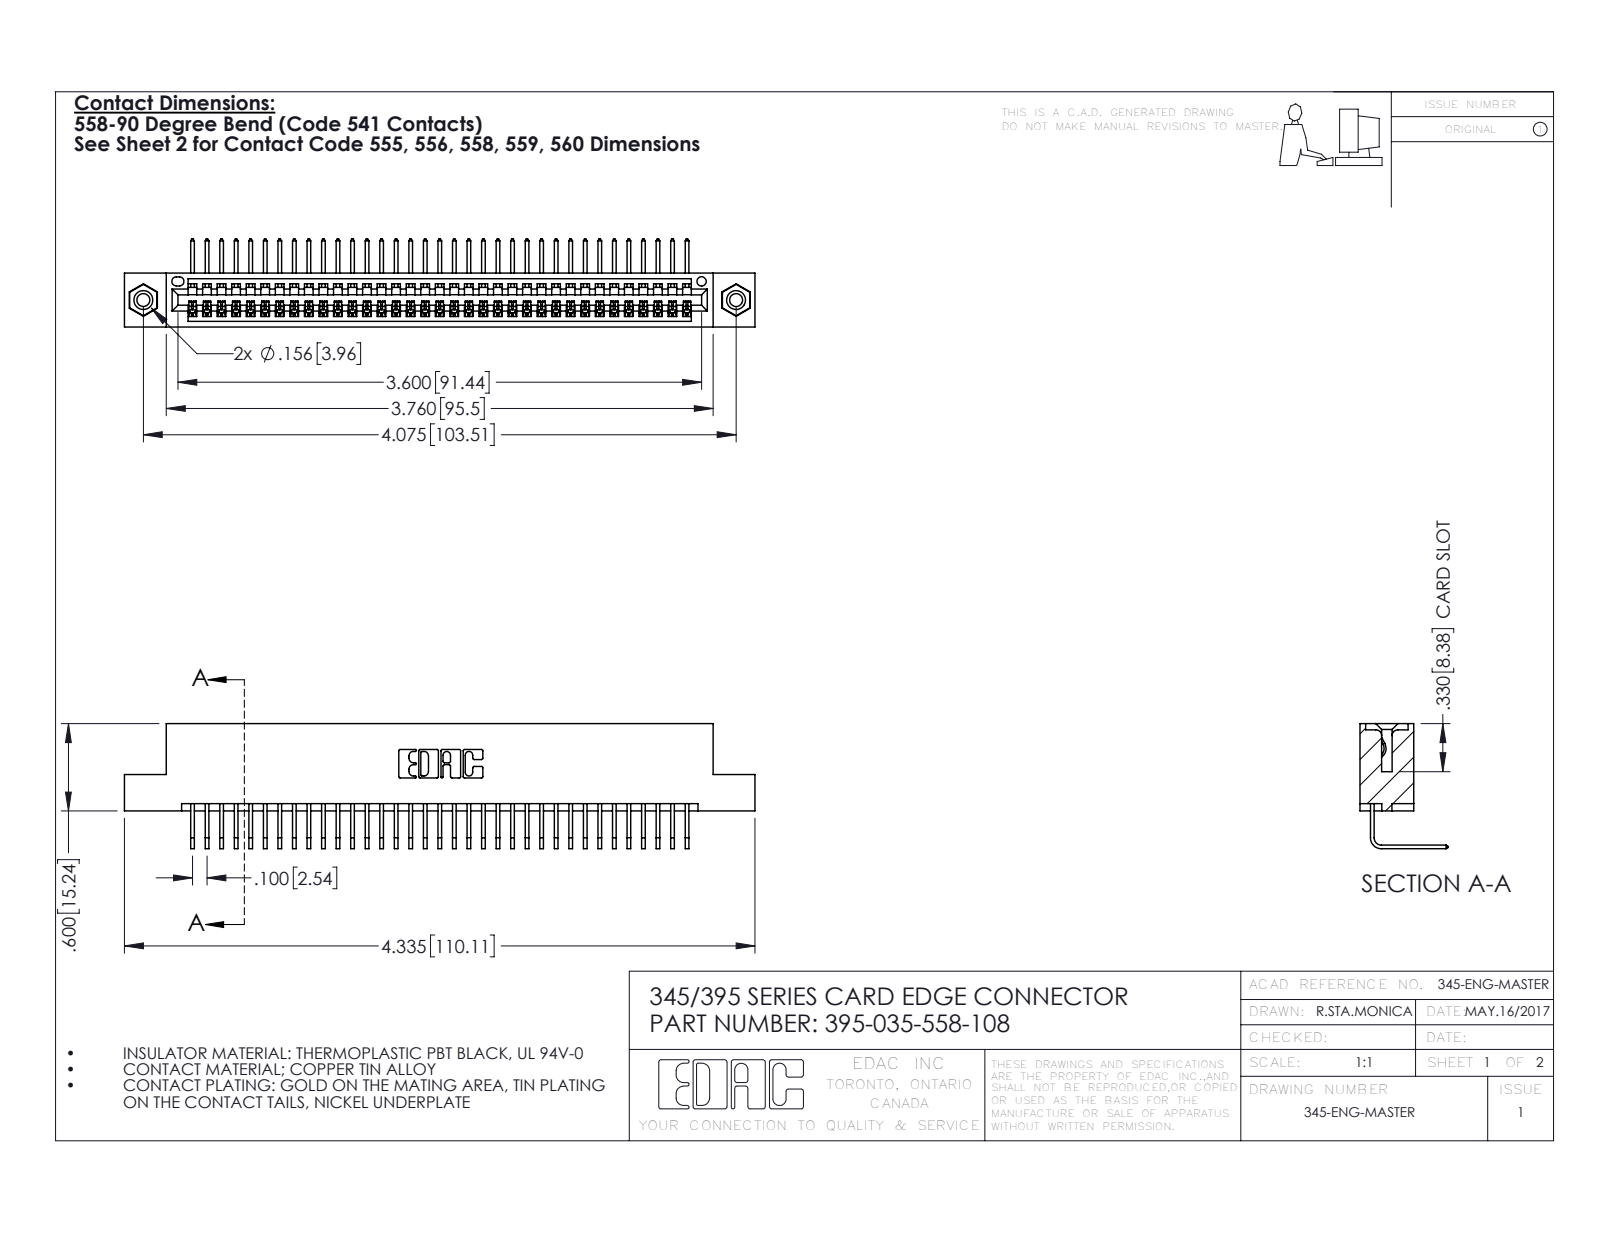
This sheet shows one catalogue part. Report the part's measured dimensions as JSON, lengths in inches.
{"part_name": "395-035-558-108; 345-250-001_345-250-003-102; 345-292-001_558 Tail - 2; 345 Part_Flush Mounting Lugs - 0.156 Dia-TI", "step_written_by": "SolidWorks 2016 (CONFIG_CONTROL_DESIGN)", "units": "inches", "bodies": {"solids": 38, "faces": 2286, "planar": 1582, "cylindrical": 688, "other": 16}, "overall_size": [4.335, 0.859, 0.605], "volume_in3": 0.641, "surface_area_in2": 22.6, "round_holes": [[0.089, 2], [0.125, 2], [0.156, 2], [0.064, 1]], "round_bosses_or_shafts": [[0.155, 2]], "partial_cylinders_radius": [[0.006, 70], [0.01, 22], [0.007, 6], [0.031, 6], [0.026, 3], [0.031, 2], [0.04, 2], [0.014, 1]], "face_to_face_distances": [0.072, 0.298, 0.37, 0.2, 0.098, 0.272, 0.025, 0.225, 0.149, 0.072], "hole_center_spacings": [0.27, 3.839, 4.075]}
